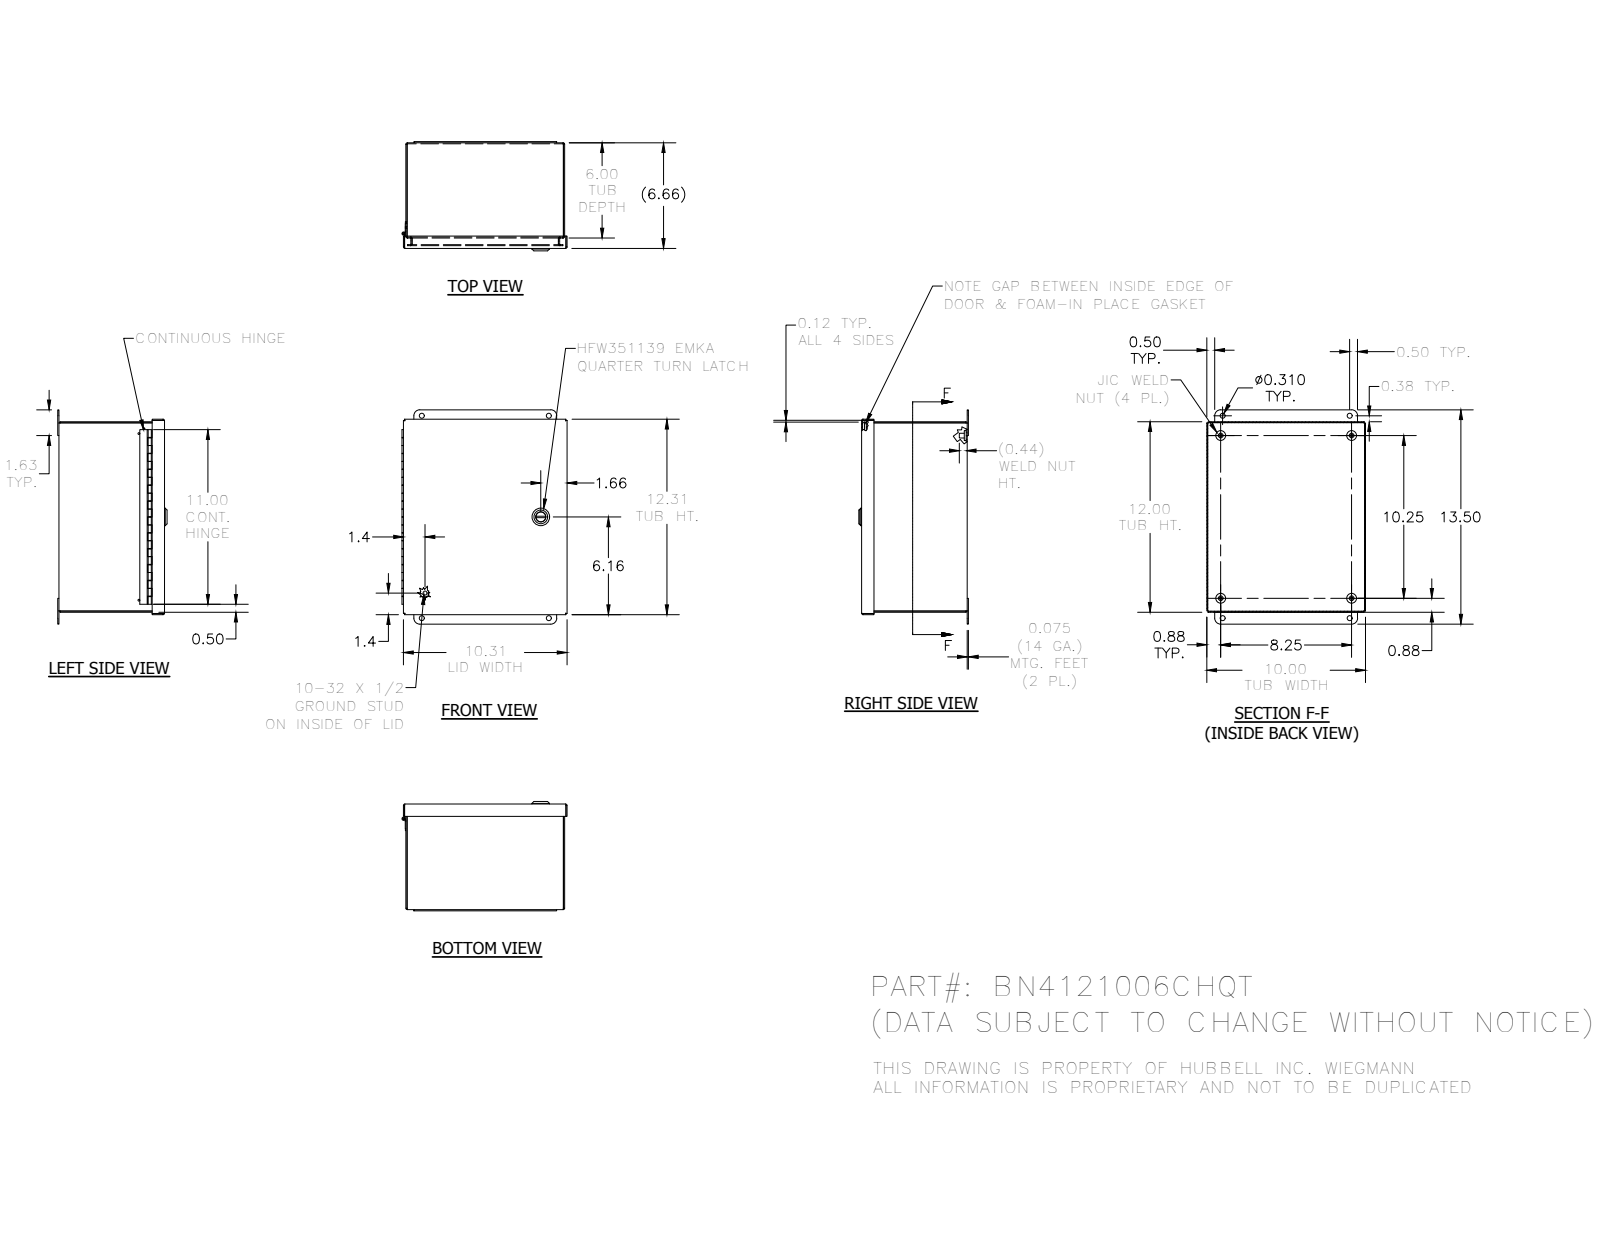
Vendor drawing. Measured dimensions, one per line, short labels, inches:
name: BN4121006CHQT
written by: SolidWorks 2018 (AUTOMOTIVE_DESIGN)
unit: in
bodies: 21 solids, 785 faces (396 planar, 261 cylindrical, 128 other)
size: 13.5 × 10.406 × 6.888
volume: 43.62 in³; area: 1 333 in²
holes: 4× ⌀0.156, 4× ⌀0.31, 3× ⌀0.12, 1× ⌀0.116, 1× ⌀0.197, 1× ⌀0.315, 1× ⌀0.394, 1× ⌀0.402, 1× ⌀0.634, 1× ⌀0.802
bosses: 4× ⌀0.625, 4× ⌀0.3, 1× ⌀1.102, 1× ⌀0.866, 1× ⌀0.78, 1× ⌀0.622, 1× ⌀0.598, 1× ⌀0.531
rounds: 30× R0.012, 20× R0.031, 20× R0.093, 16× R0.125, 12× R0.02, 4× R0.157, 4× R0.375, 2× R0.016
face distances: 0.062, 0.062, 6.594, 6.656, 6.532, 6.594, 11.938, 9.938, 10, 9.876
hole spacings: 14.081, 1.256, 8, 8.22, 8.221, 8.25, 9.84, 10.25
